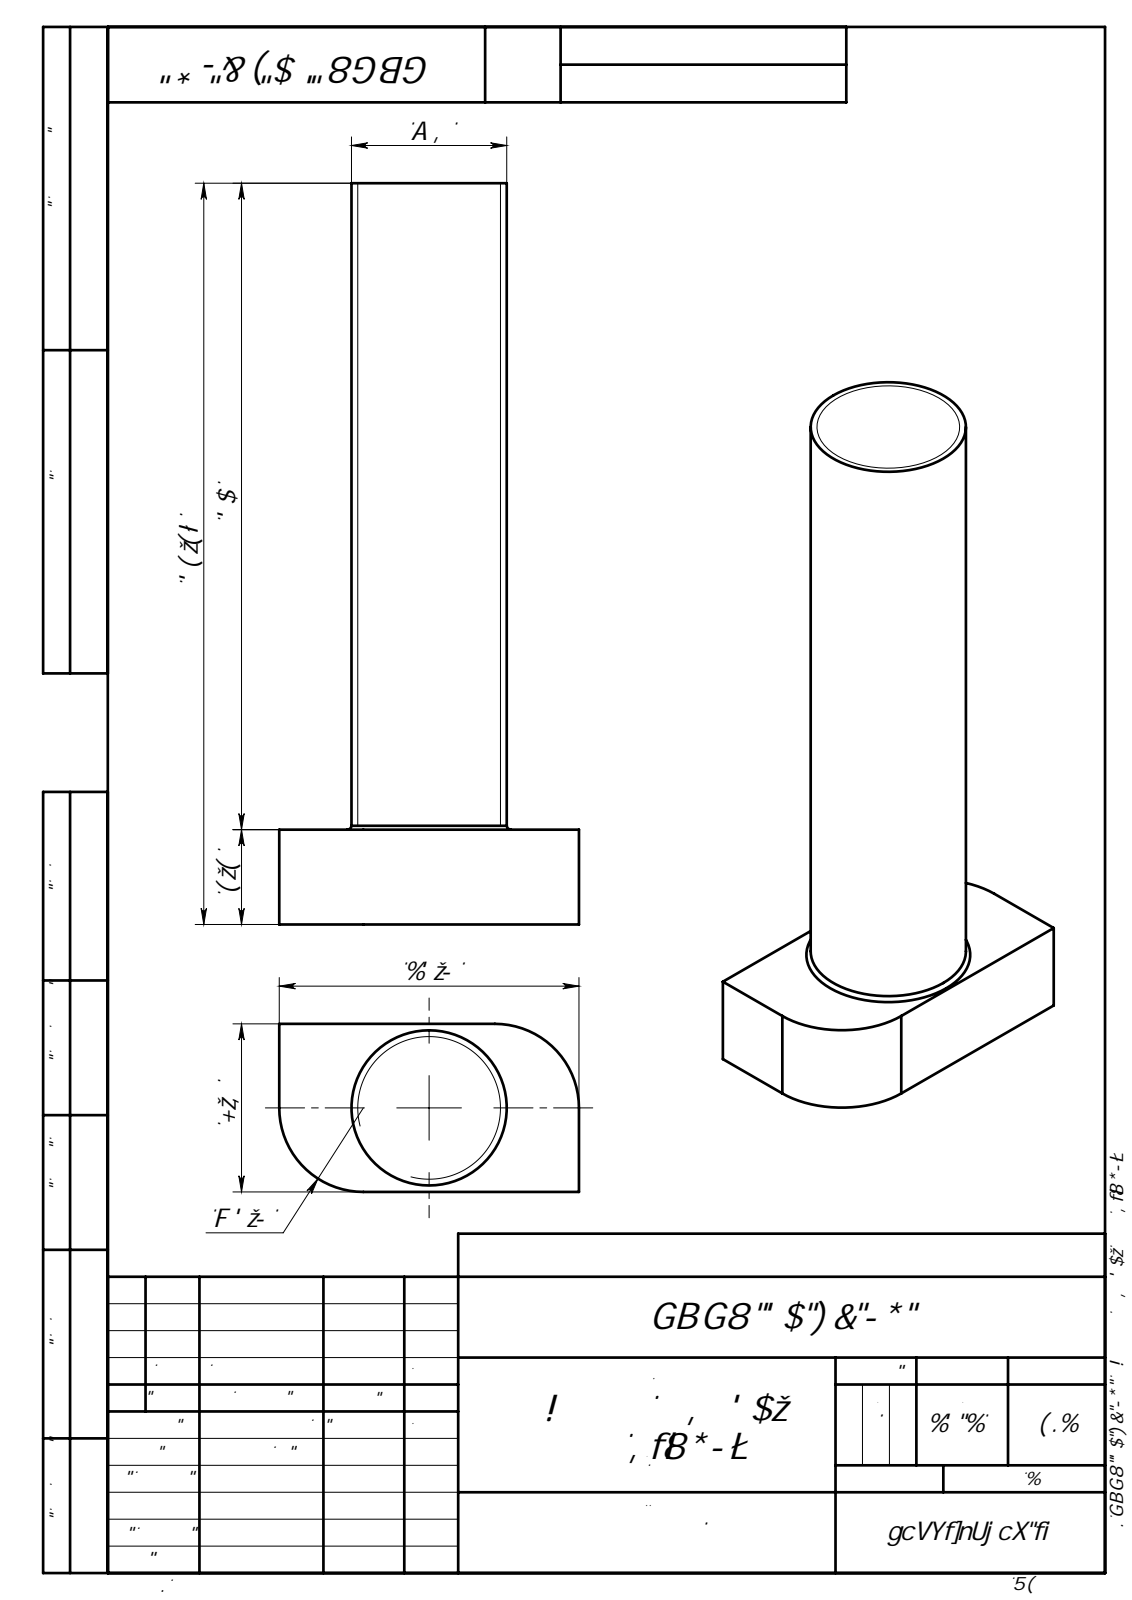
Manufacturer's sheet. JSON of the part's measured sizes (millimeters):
{"part_name": "SNSD.30.52.96. Т-Болт М8х30, паз 8(D69)", "step_written_by": "SolidWorks 2014 (AUTOMOTIVE_DESIGN)", "units": "millimeters", "bodies": {"solids": 1, "faces": 13, "planar": 7, "cylindrical": 4, "other": 2}, "overall_size": [34.4, 13.9, 7.8], "volume_mm3": 1670, "surface_area_mm2": 1057, "round_bosses_or_shafts": [[7.2, 1]], "partial_cylinders_radius": [[3.9, 2]], "face_to_face_distances": [4.4, 7.8, 34.4, 30, 13.9]}
